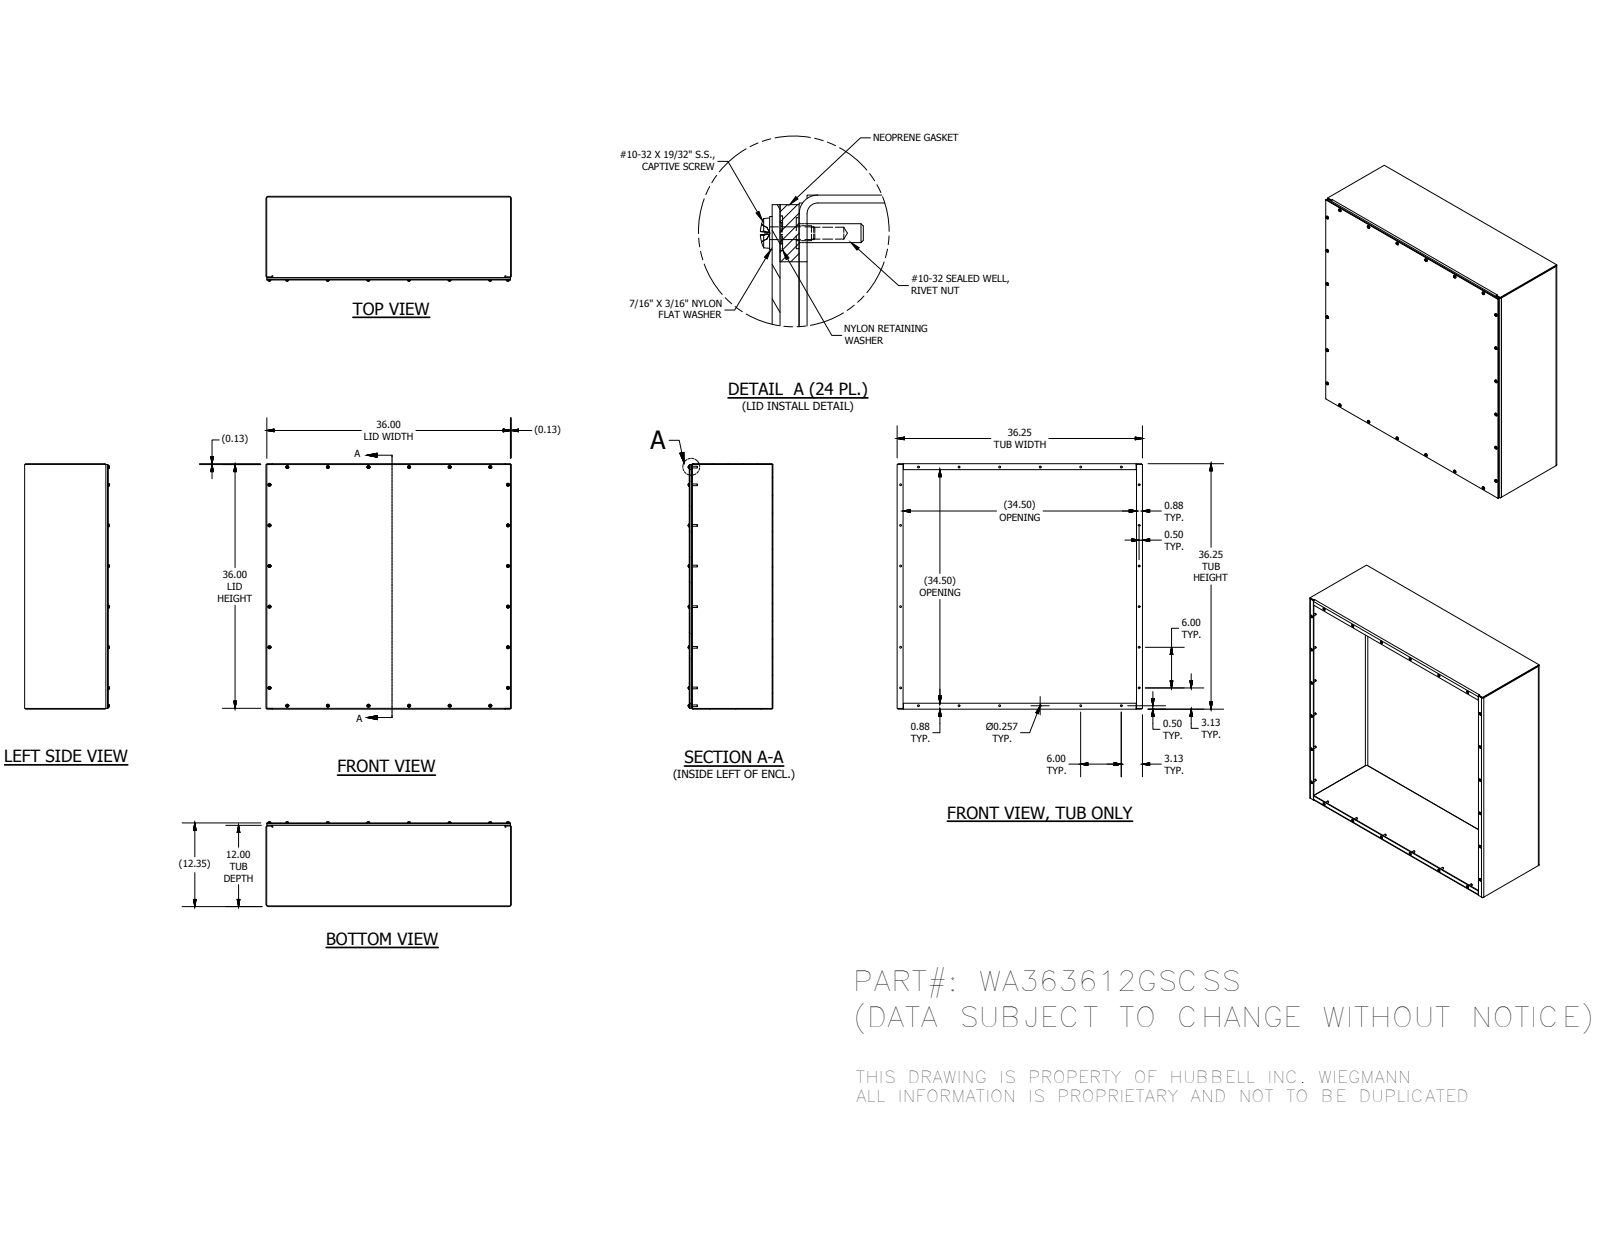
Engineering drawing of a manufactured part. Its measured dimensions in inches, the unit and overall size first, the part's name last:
Units: inches
Overall size (bounding box): 36.25 × 36.25 × 12.509
Round holes (diameter × count): ⌀0.156 ×24, ⌀0.188 ×24, ⌀0.196 ×24, ⌀0.257 ×24, ⌀0.278 ×24, ⌀0.281 ×24
Round bosses / shafts (diameter × count): ⌀0.453 ×24, ⌀0.437 ×24, ⌀0.406 ×24, ⌀0.248 ×24, ⌀0.167 ×24
Partial cylindrical surfaces — rounded edges, fillets, slot ends (radius × count): R0.089 ×24, R0.031 ×4, R0.141 ×4, R0.244 ×4, R0.016 ×2, R0.25 ×2, R0.354 ×2
Main face-to-face distances: 0.104, 12.25, 12.146, 12.354, 0.104, 36.146, 36.042, 36.25, 36.146, 36.25
Hole centre spacings: 6, 12, 18, 35.757, 24, 35.757, 37.237, 35.25
Volume: 485.7 in³ · Surface area: 9 210 in²
Bodies: 101 solids, 2018 faces (1134 planar, 380 cylindrical, 504 other)
Part name (STEP PRODUCT): WA363612GSCSSBLR; WA3612GSCSSTB; WA3636GSCSSLID; WA3636GSCSSSTRIPGSK (+5 more)
STEP written by: Autodesk Inventor 2016 (AUTOMOTIVE_DESIGN)
